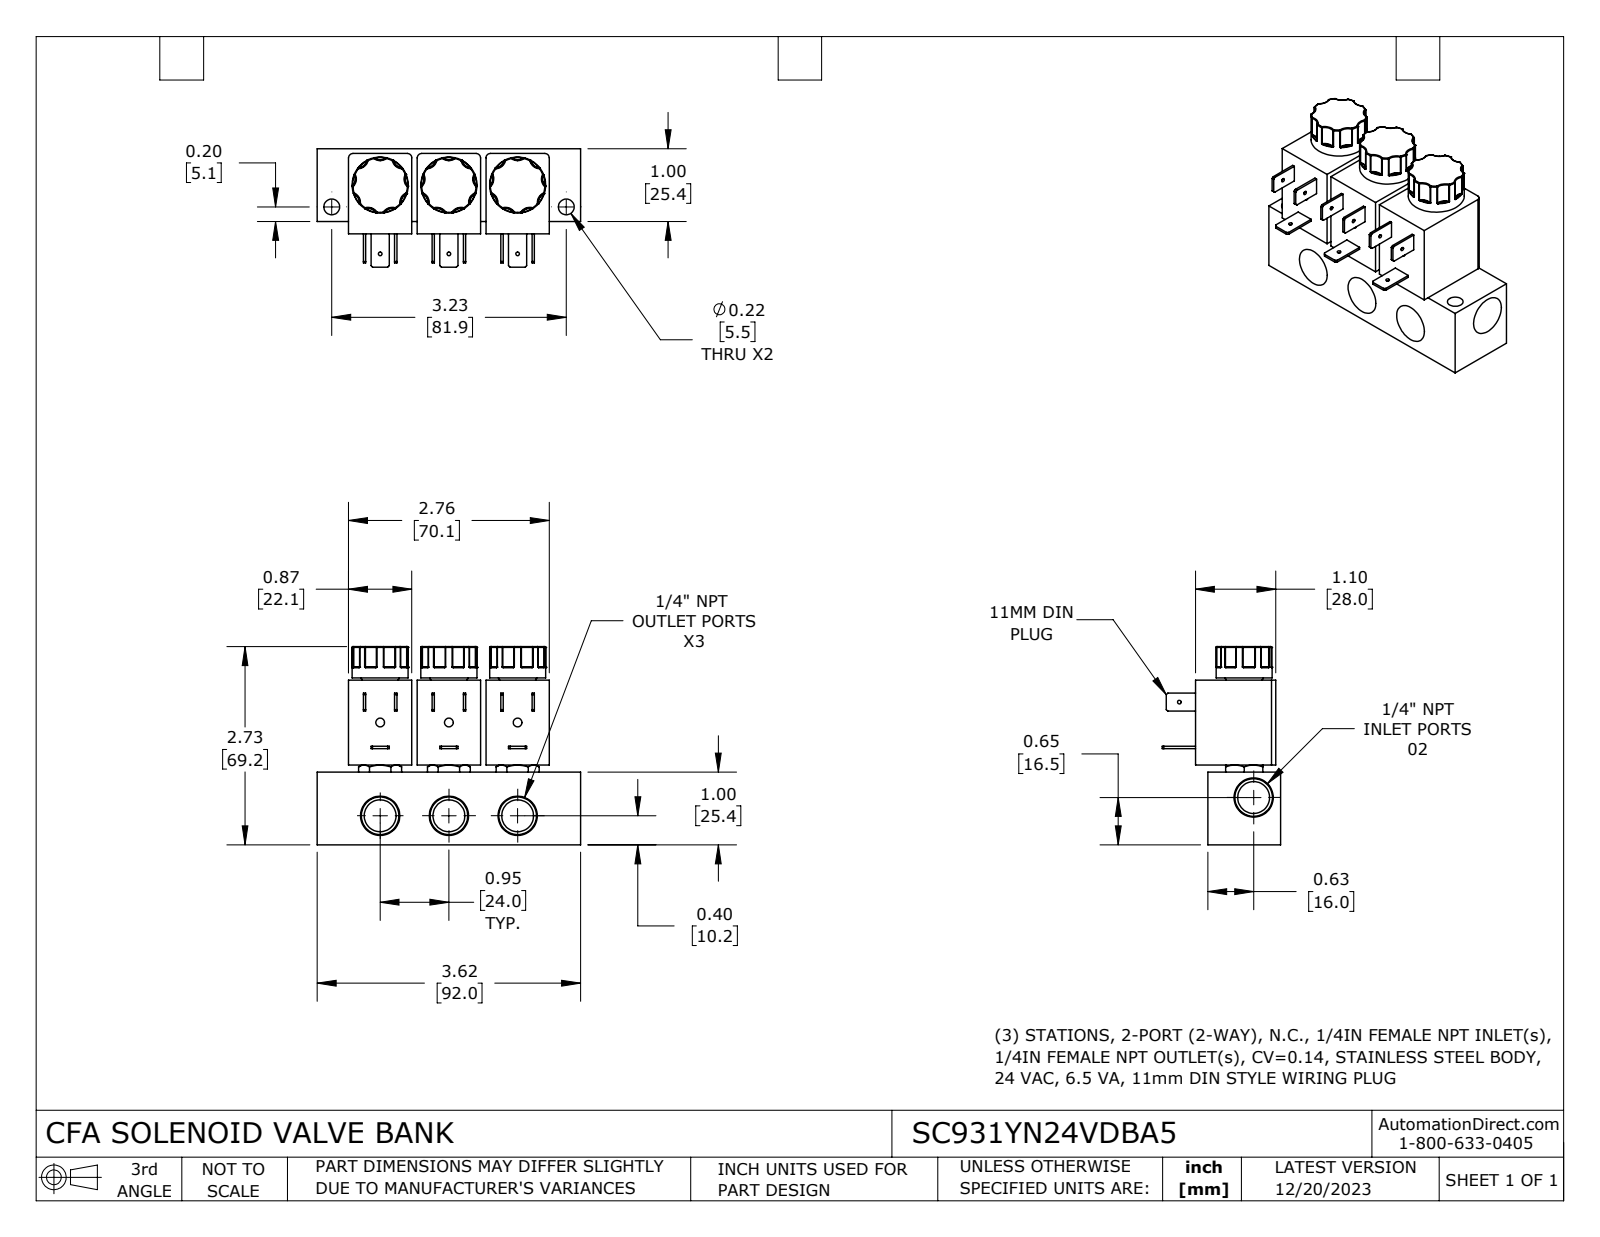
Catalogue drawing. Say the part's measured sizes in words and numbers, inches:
The part is named "SC931YN24VDBA5". Its 3-D file was written by "SolidWorks 2023 (CONFIG_CONTROL_DESIGN)". It is 1 solid with 657 faces: 146 planar, 140 cylindrical and 371 other. Overall it measures 3.622 by 2.725 by 1.627 inches. Its volume is 7.008 cubic inches and its surface area 47.81 square inches. Round holes: 4 of diameter 0.05, 4 of diameter 0.438, 3 of diameter 0.12, 2 of diameter 0.217. Round bosses or shafts: 3 of diameter 0.77. Partial cylindrical surfaces (rounded edges, fillets, slot ends): 54 of radius 0.01, 25 of radius 0.133, 6 of radius 0.06, 2 of radius 0.132. The main face-to-face distances are 1, 0.945, 0.87, 1.169, 0.169, 0.065, 0.935, 1.104, 1.89, 1.815. The hole center spacings are 0.945, 1.593, 1.282, 1.89, 2.283, 0.928, 0.93, 1.662.
